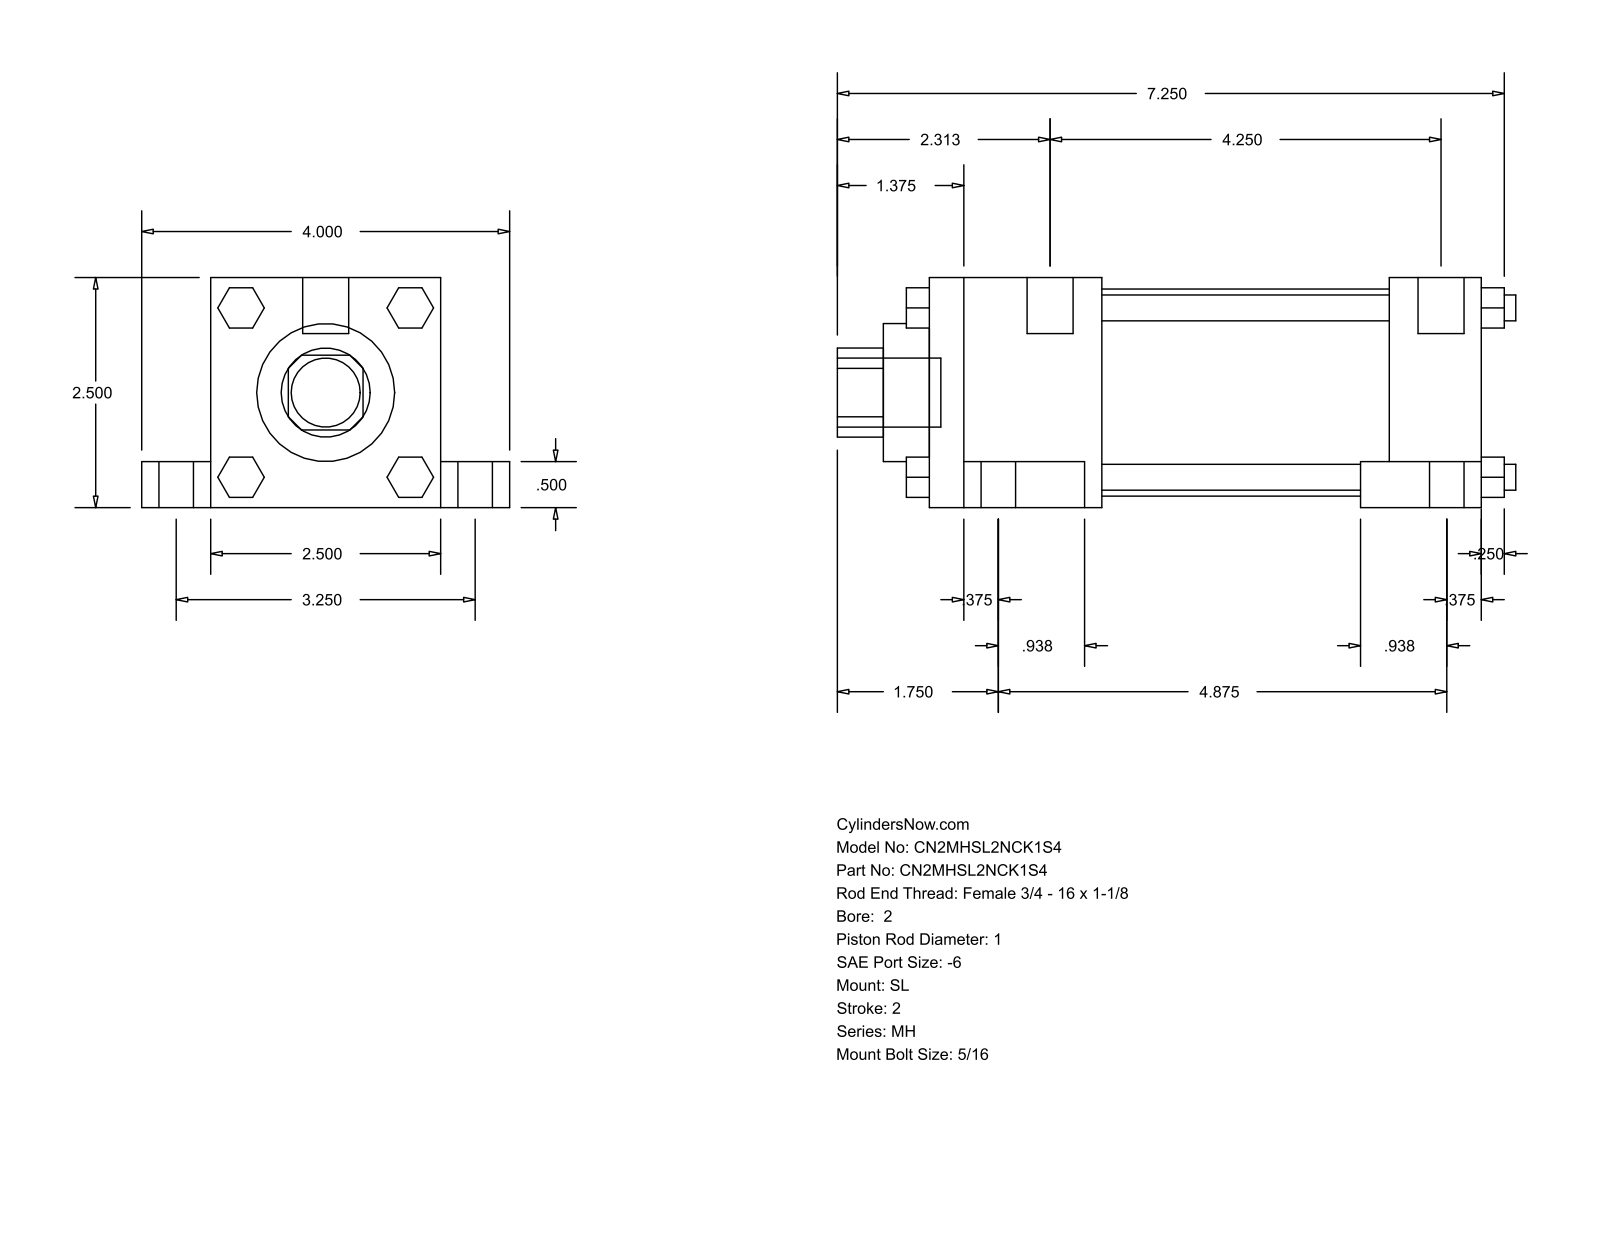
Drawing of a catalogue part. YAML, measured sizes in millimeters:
part_name: "MH_SL__0200_1"
step_written_by: "GSSL Pune (CONFIG_CONTROL_DESIGN)"
units: millimeters
bodies: {solids: 0, faces: 148, planar: 112, cylindrical: 36, other: 0}
overall_size: [187.32, 101.6, 63.5]
round_holes:
  - {diameter: 25.4, count: 1}
  - {diameter: 38.1, count: 1}
  - {diameter: 57.15, count: 1}
round_bosses_or_shafts:
  - {diameter: 15.88, count: 4}
  - {diameter: 9.53, count: 4}
  - {diameter: 7.14, count: 4}
  - {diameter: 5.56, count: 4}
  - {diameter: 12.7, count: 2}
  - {diameter: 19.05, count: 1}
partial_cylinders:
  - {radius: 12.29, count: 1}
face_to_face_distances: [63.5, 152.4, 12.7, 19.05, 50.8, 82.55, 9.52, 25.4, 127, 47.63]
